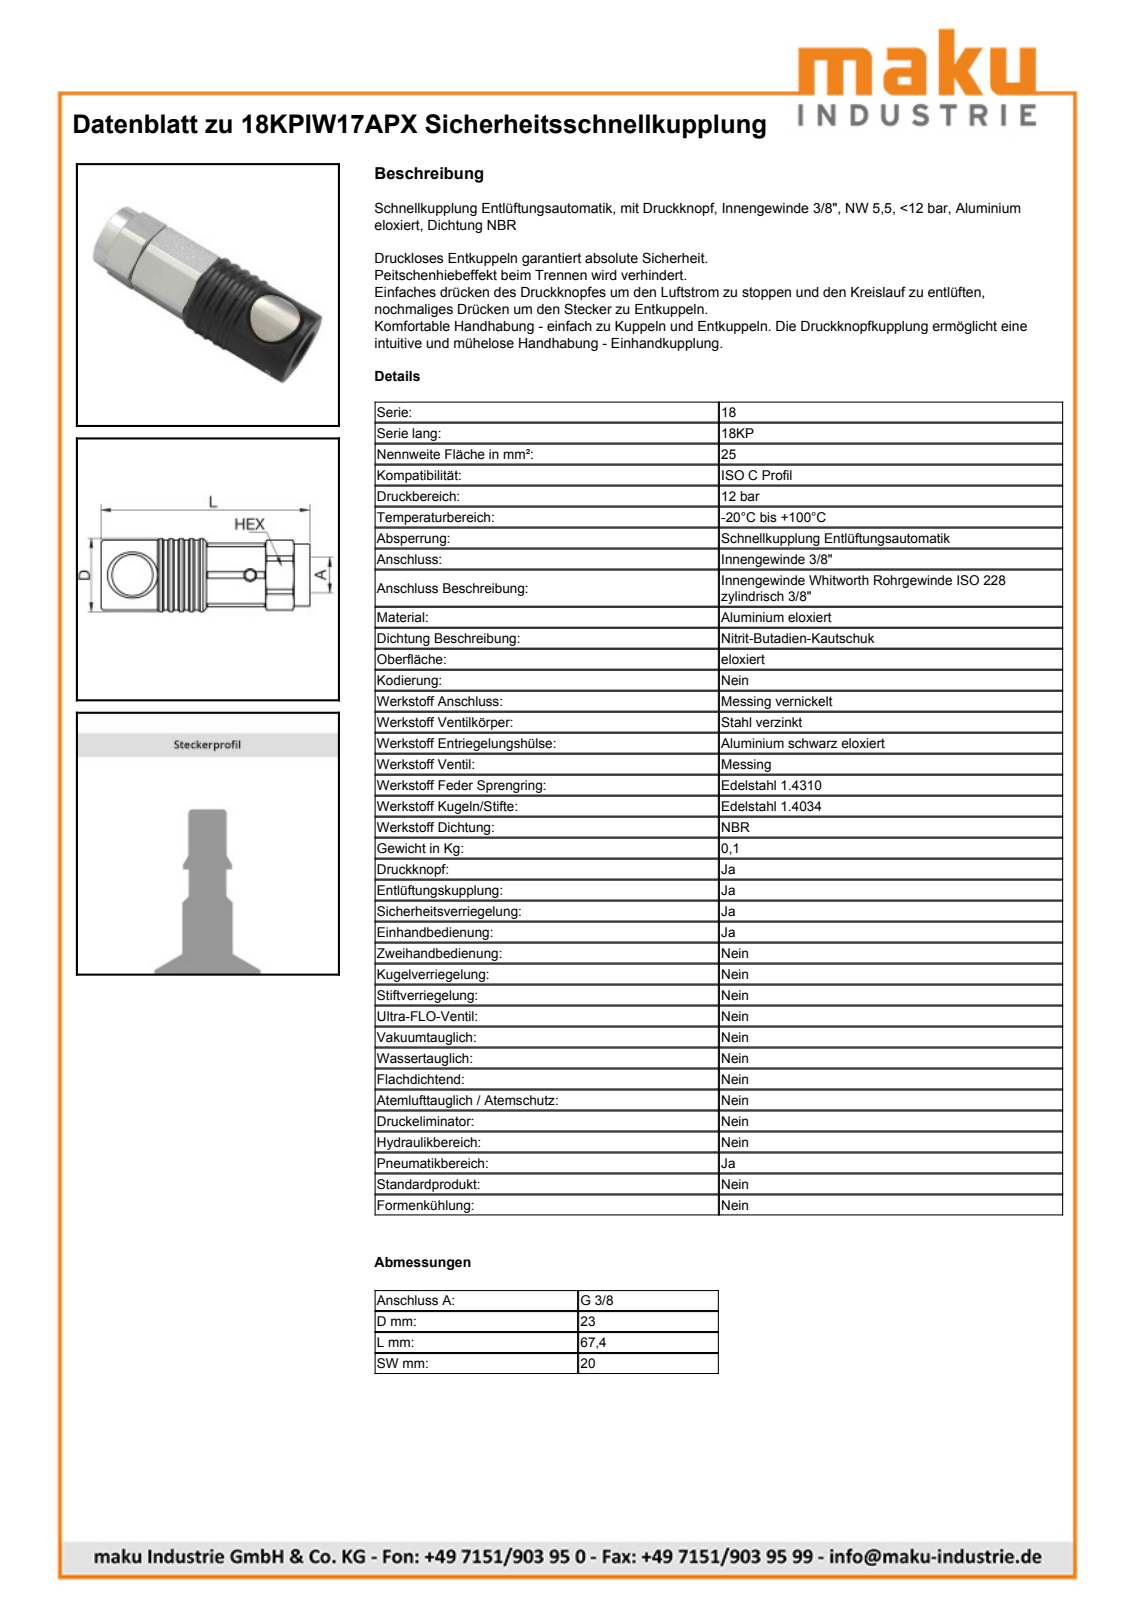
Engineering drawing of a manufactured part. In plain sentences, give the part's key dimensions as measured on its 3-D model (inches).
The part is named "18KPIW17APX". Its 3-D file was written by "Autodesk Inventor 2019 (CONFIG_CONTROL_DESIGN)". It is 27 solids with 296 faces: 94 planar, 107 cylindrical and 95 other. Overall it measures 2.654 by 0.906 by 0.906 inches. Its volume is 1.608 cubic inches and its surface area 30.11 square inches. Round holes: 1 of diameter 0.098, 1 of diameter 0.138, 1 of diameter 0.217, 1 of diameter 0.276, 1 of diameter 0.335, 1 of diameter 0.398, 1 of diameter 0.409, 1 of diameter 0.413, 1 of diameter 0.437, 1 of diameter 0.508, 1 of diameter 0.553, 1 of diameter 0.591. Round bosses or shafts: 1 of diameter 0.906, 1 of diameter 0.866, 1 of diameter 0.787, 1 of diameter 0.768, 1 of diameter 0.728, 1 of diameter 0.717, 1 of diameter 0.709, 1 of diameter 0.646. Partial cylindrical surfaces (rounded edges, fillets, slot ends): 1 of radius 0.148, 1 of radius 0.284, 1 of radius 0.307, 1 of radius 0.433, 1 of radius 0.487. The main face-to-face distances are 0.787, 1.157, 2.063, 0.906, 0.433, 0.748, 0.177, 0.276, 0.098, 1.168. The hole center spacings are 0.047, 0.049, 1.474.
